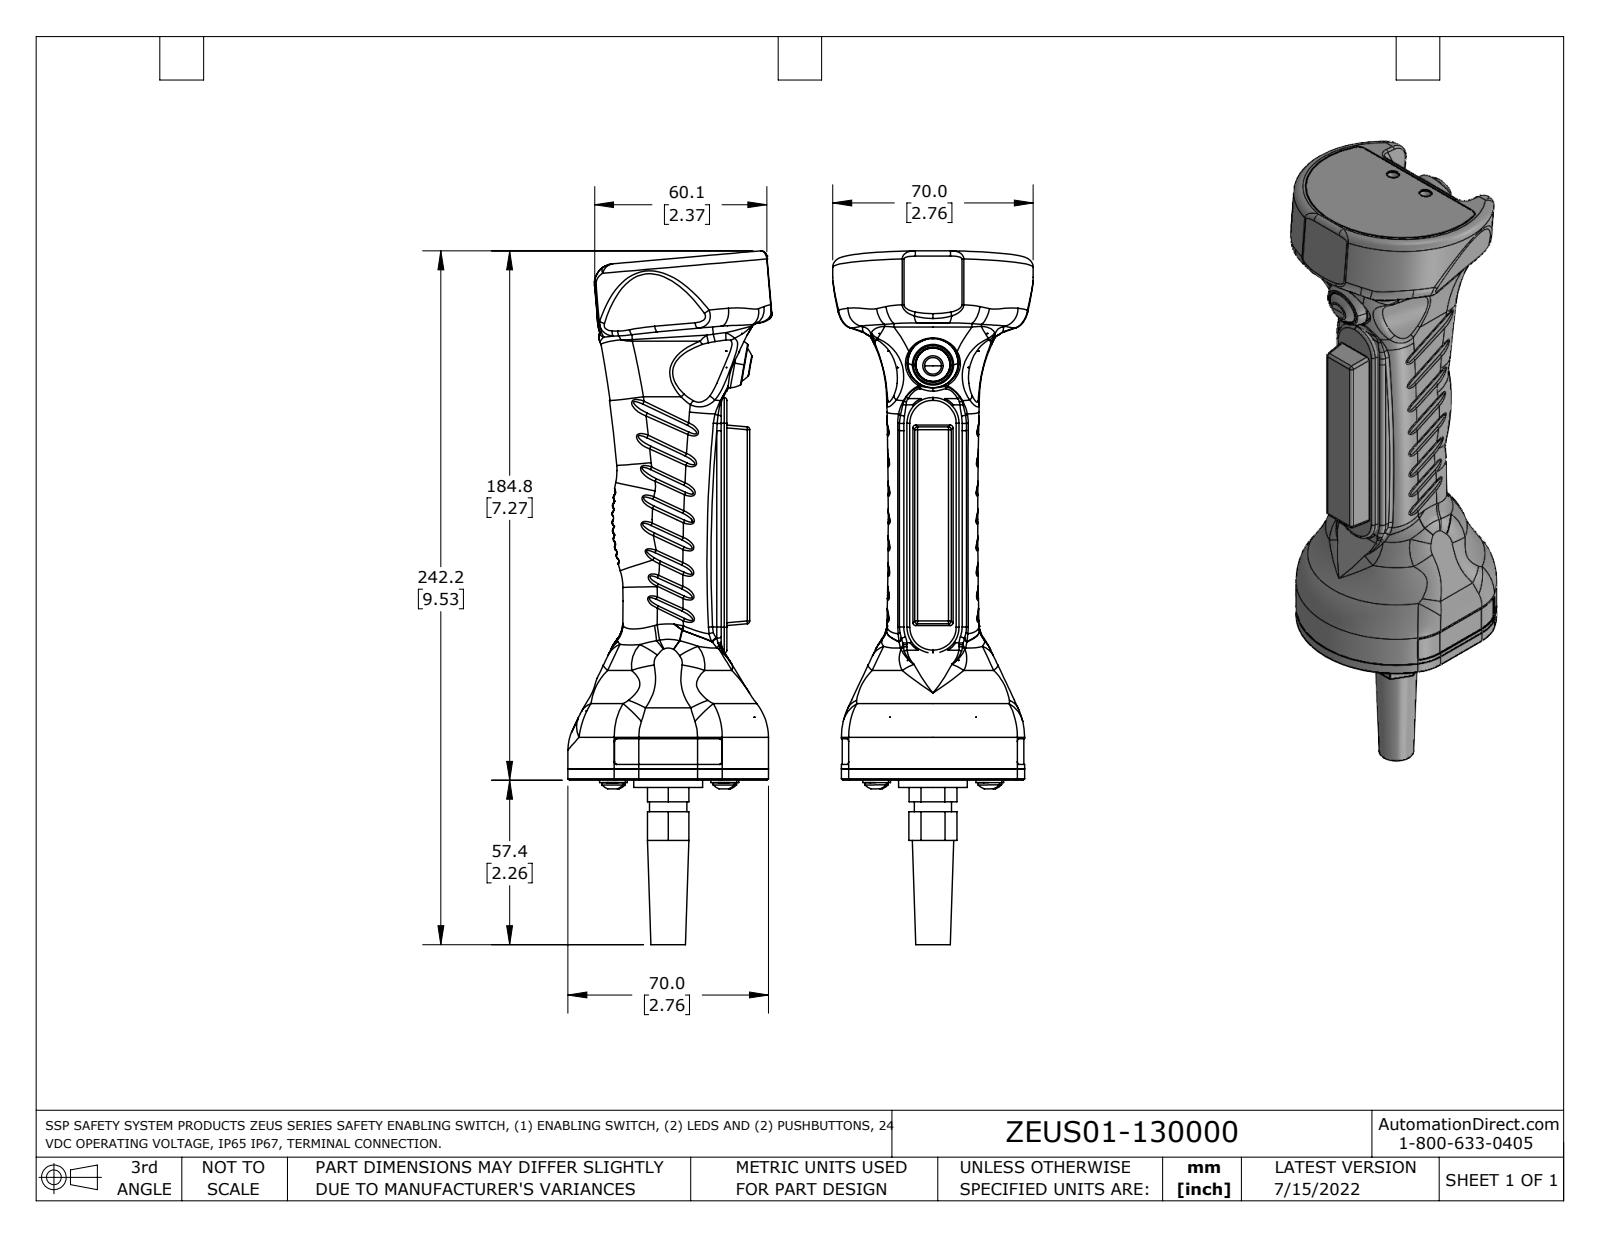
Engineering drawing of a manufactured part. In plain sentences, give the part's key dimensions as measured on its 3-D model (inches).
The part is named "ZEUS01-130000". Its 3-D file was written by "SolidWorks 2021 (AUTOMOTIVE_DESIGN)". It is 19 solids with 1595 faces: 615 planar, 508 cylindrical and 472 other. Overall it measures 9.535 by 2.803 by 2.756 inches. Its volume is 23.41 cubic inches and its surface area 123.8 square inches. Round holes: 4 of diameter 0.132, 4 of diameter 0.169, 4 of diameter 0.177, 4 of diameter 0.197, 2 of diameter 0.039, 2 of diameter 0.098, 2 of diameter 0.11, 2 of diameter 0.159, 2 of diameter 0.165, 2 of diameter 0.173, 2 of diameter 0.201, 2 of diameter 0.205. Round bosses or shafts: 4 of diameter 0.354, 4 of diameter 0.295, 4 of diameter 0.157, 4 of diameter 0.039, 3 of diameter 0.461, 2 of diameter 0.689, 2 of diameter 0.472, 2 of diameter 0.406. Partial cylindrical surfaces (rounded edges, fillets, slot ends): 96 of radius 0.005, 51 of radius 0.039, 48 of radius 0.028, 42 of radius 0.008, 21 of radius 0.079, 16 of radius 0.006, 10 of radius 0.118, 7 of radius 0.031. The main face-to-face distances are 0.157, 0.079, 0.02, 0.014, 0.065, 0.059, 0.098, 0.177, 0.571, 0.256. The hole center spacings are 1.531, 0.63, 1.181, 1.558, 2.184, 0.404, 0.404, 0.513.
